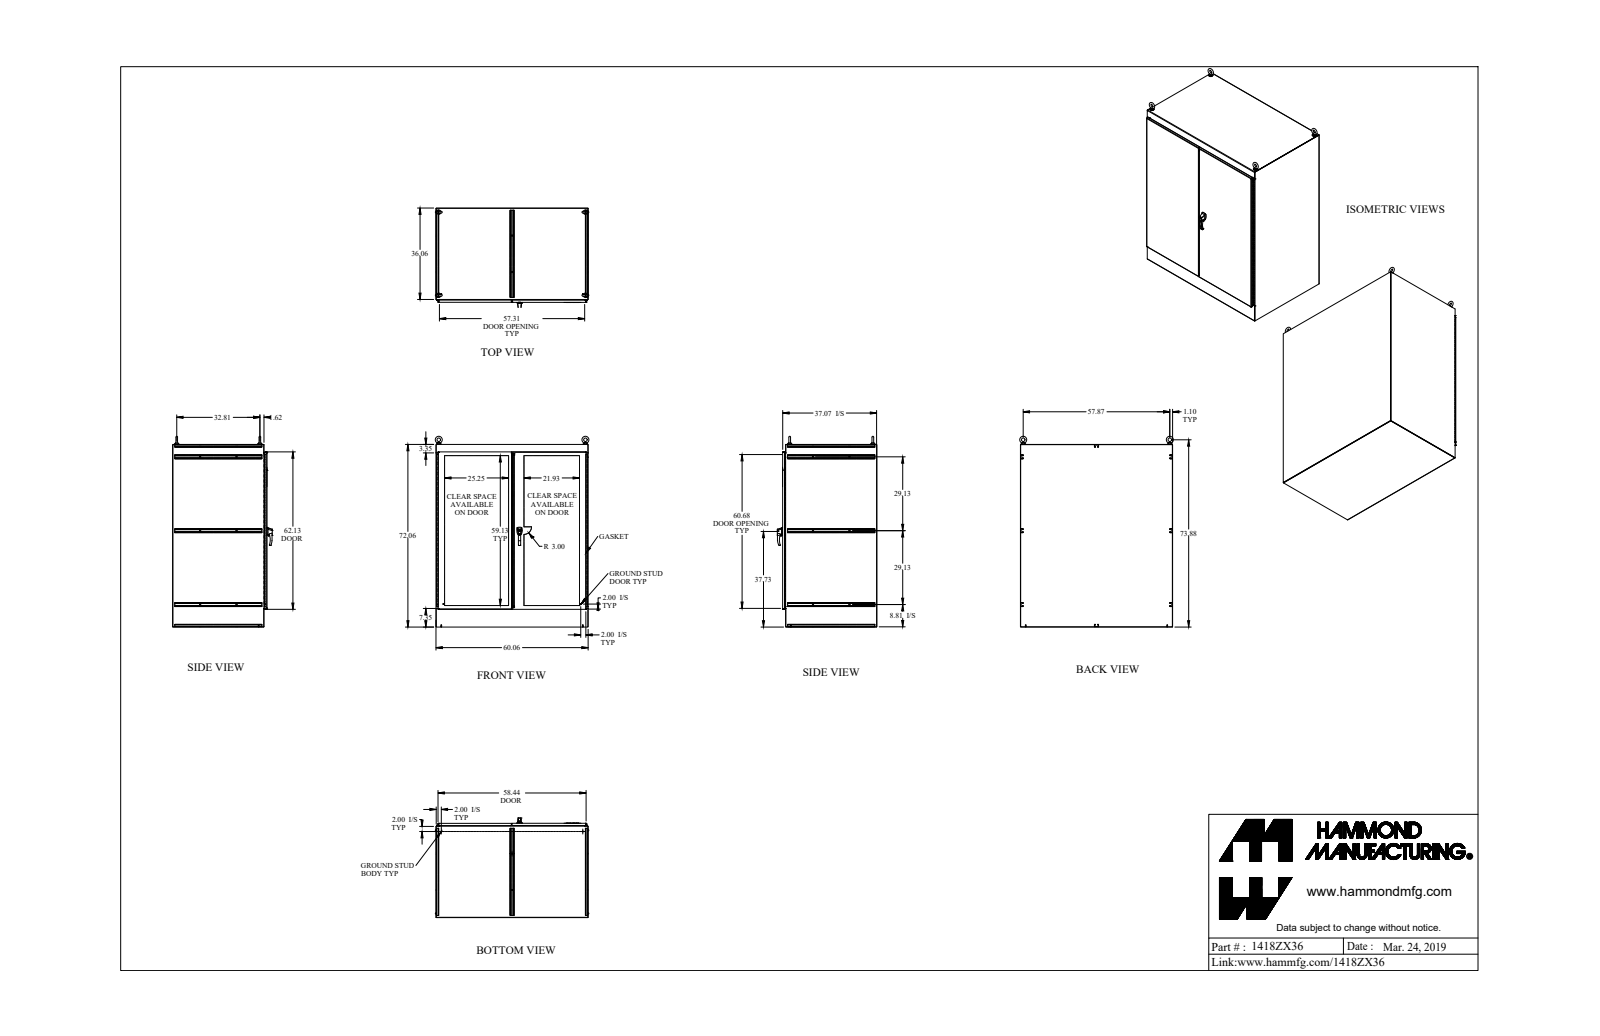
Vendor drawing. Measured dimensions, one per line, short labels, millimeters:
name: 1418ZX36_Default
written by: SolidWorks 2019 (CONFIG_CONTROL_DESIGN)
unit: mm
bodies: 79 solids, 2723 faces (1226 planar, 1272 cylindrical, 225 other)
size: 1923.1 × 1552.4 × 999.2
volume: 35 970 000 mm³; area: 27 870 000 mm²
holes: 20× ⌀7.7, 8× ⌀12.7, 4× ⌀13.4, 4× ⌀15.9, 4× ⌀17.4, 4× ⌀19.1, 2× ⌀2.8, 2× ⌀6.4, 2× ⌀6.5, 2× ⌀7.1, 2× ⌀7.1, 2× ⌀8
bosses: 6× ⌀7.1, 4× ⌀44.5, 4× ⌀38.1, 4× ⌀31.8, 4× ⌀18.7, 4× ⌀6.4, 2× ⌀25.4, 2× ⌀19.1
rounds: 54× R1.1, 48× R3.5, 22× R3.2, 20× R1.2, 20× R3.6, 16× R0.5, 10× R1.5, 8× R1.3
face distances: 2.4, 1523.1, 3.2, 1827.9, 939.9, 943, 942.3, 945.4, 1520.7, 1525.5
hole spacings: 152.4, 1489.4, 304.8, 1512.6, 457.2, 1550.5, 609.6, 1602.1
